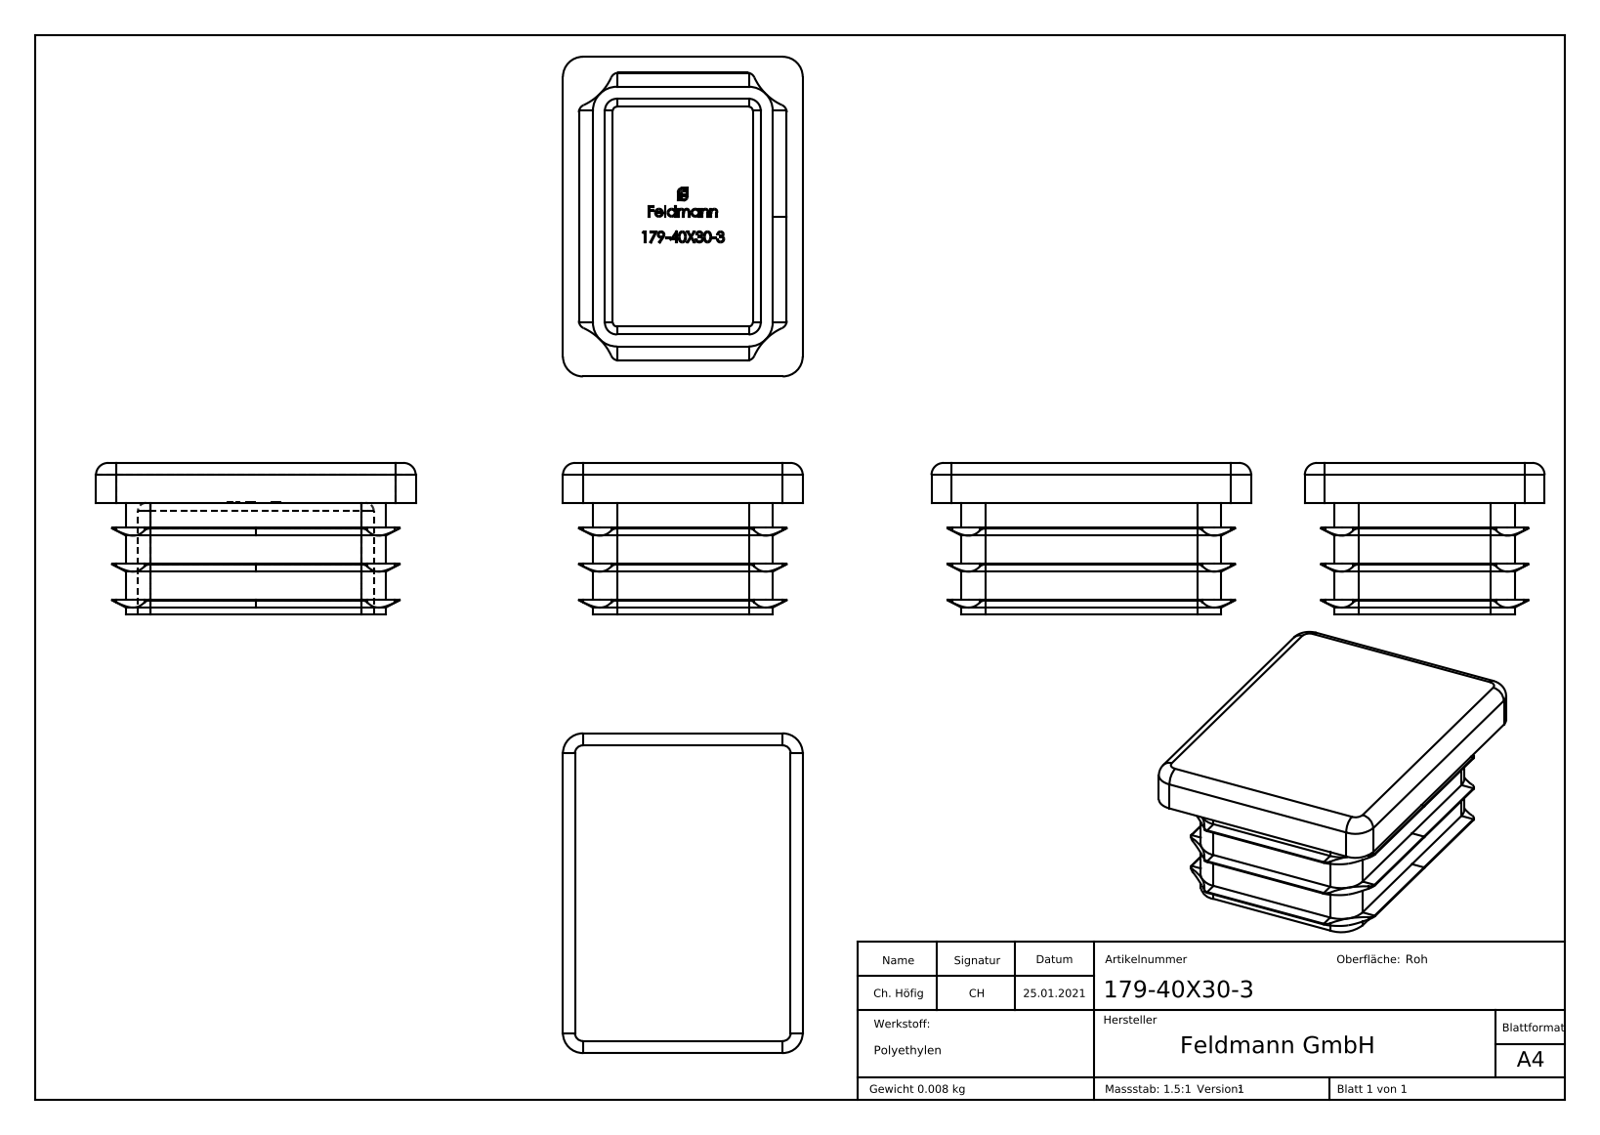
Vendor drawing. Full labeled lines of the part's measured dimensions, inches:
Part name (STEP PRODUCT): 179-40X30-3
STEP written by: SolidWorks 2018 (CONFIG_CONTROL_DESIGN)
Units: inches
Bodies: 1 solid, 523 faces (237 planar, 83 cylindrical, 203 other)
Overall size (bounding box): 1.575 × 1.181 × 0.748
Volume: 0.507 in³ · Surface area: 10.15 in²
Partial cylindrical surfaces — rounded edges, fillets, slot ends (radius × count): R0.039 ×12, R0.059 ×8, R0.098 ×4, R0.118 ×4, R0.276 ×4
Main face-to-face distances: 0.059, 0.197, 0.827, 0.148, 0.207, 1.22, 0.768, 0.177, 0.886, 0.157
